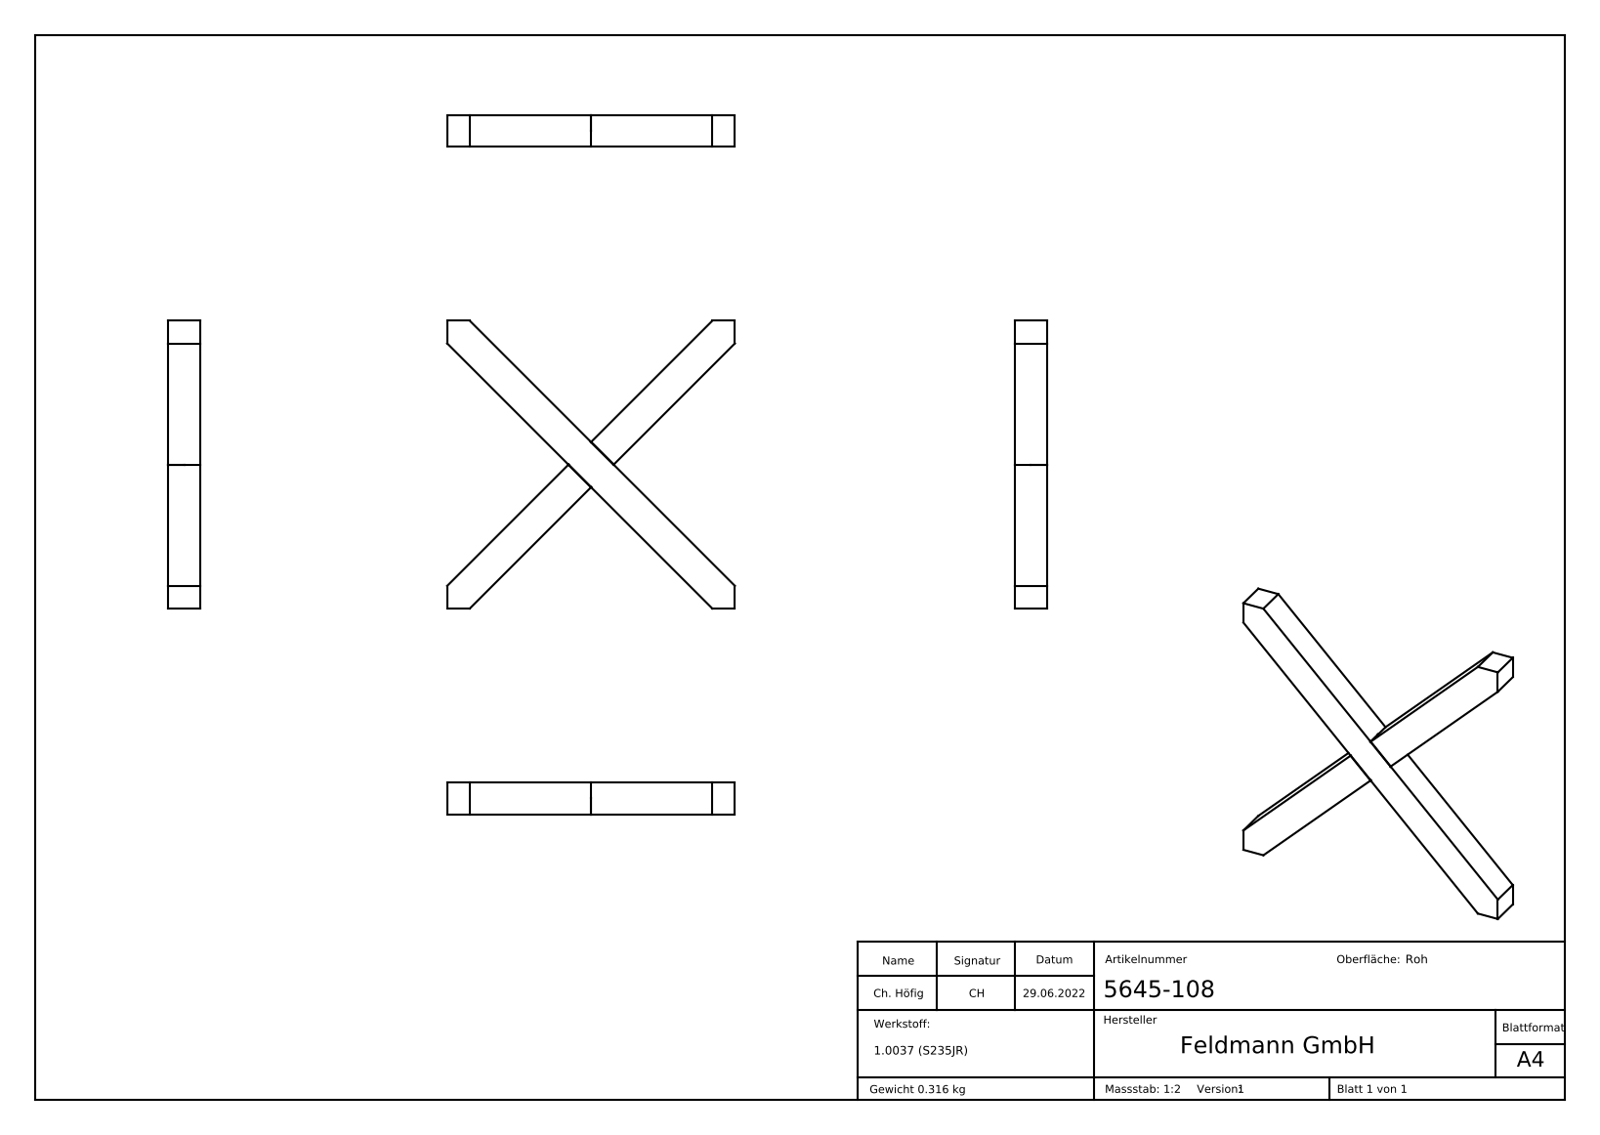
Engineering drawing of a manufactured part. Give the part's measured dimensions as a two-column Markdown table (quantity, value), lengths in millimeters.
| quantity | value |
| --- | --- |
| part name | 5645-108 |
| STEP written by | SolidWorks 2018 (CONFIG_CONTROL_DESIGN) |
| units | millimeters |
| bodies | 1 solid, 288 faces (169 planar, 0 cylindrical, 119 other) |
| overall size | 108 × 108 × 12 |
| volume | 40 517 mm³ |
| surface area | 14 044 mm² |
| main face-to-face distances | 12, 108, 11.95, 12.05, 12.1, 11.9, 6, 12.15, 12.2, 0.83 |
